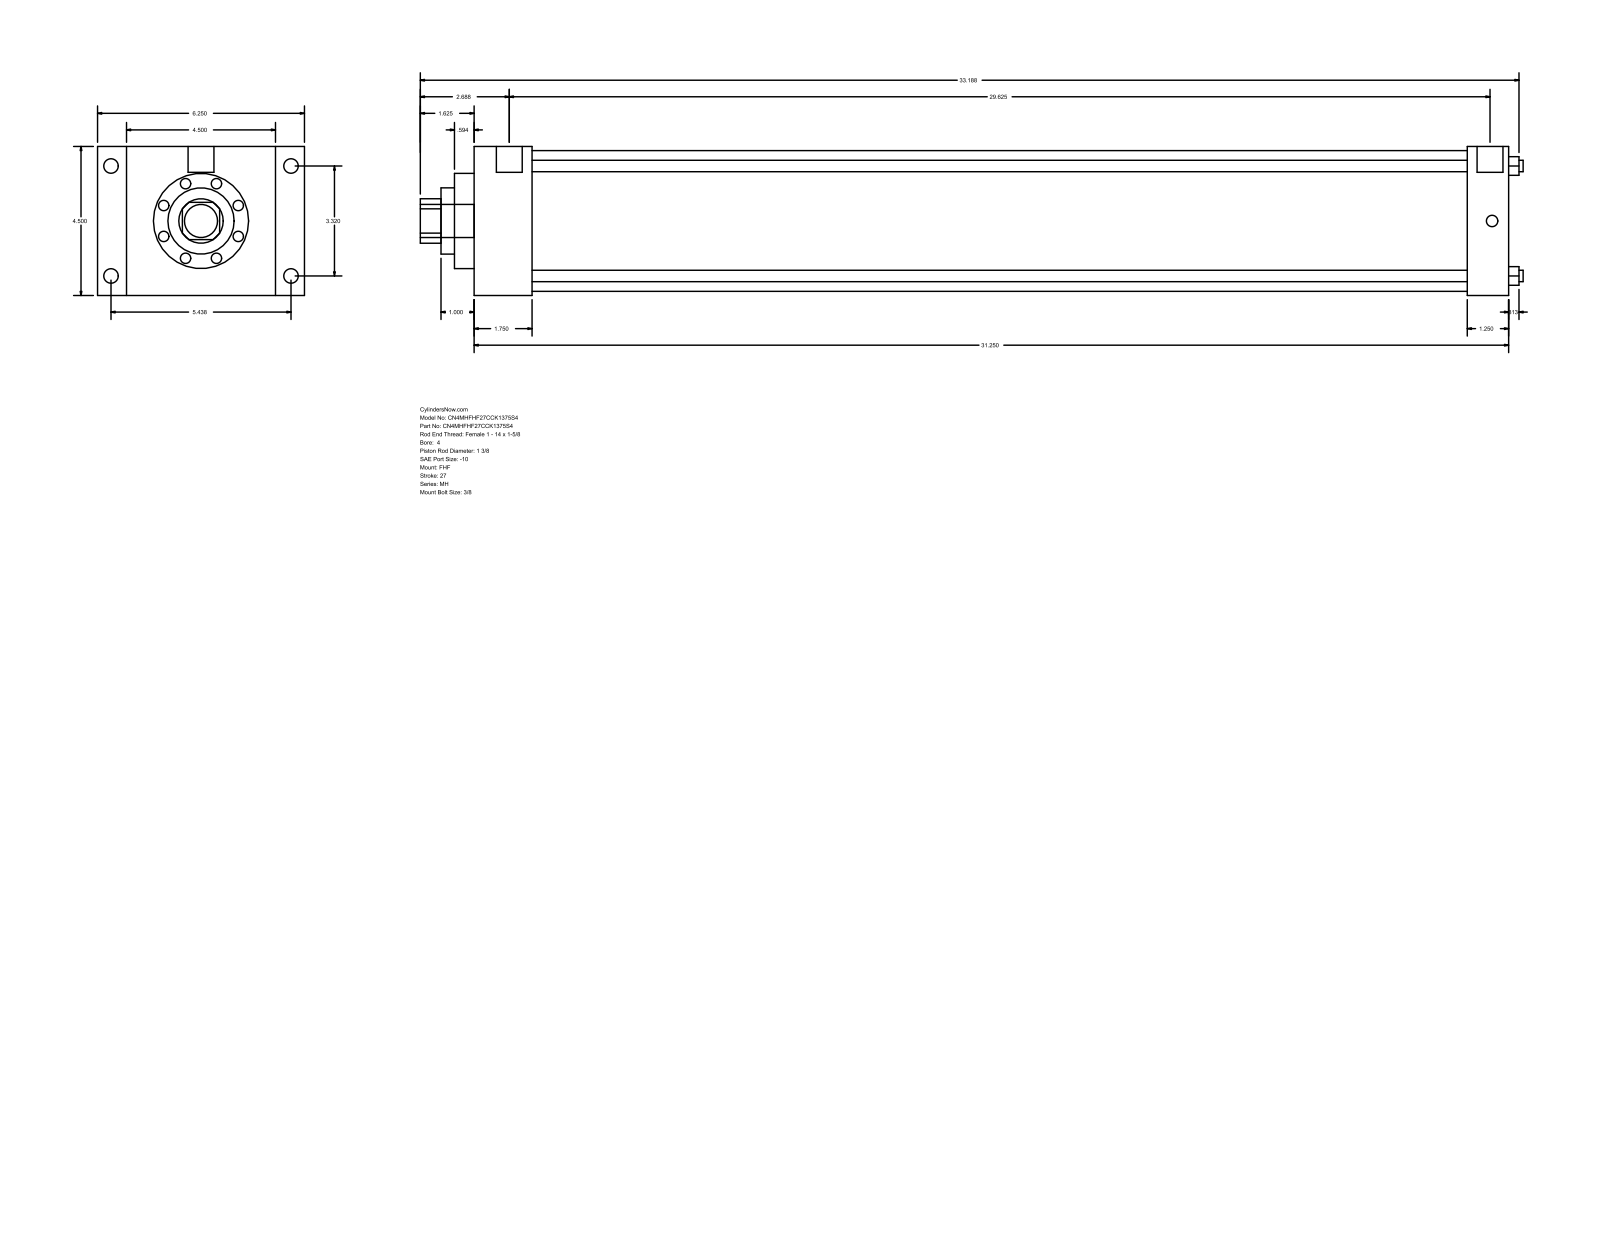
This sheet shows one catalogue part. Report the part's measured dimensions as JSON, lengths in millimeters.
{"part_name": "MH_FHF__0400_1.375", "step_written_by": "GSSL Pune (CONFIG_CONTROL_DESIGN)", "units": "millimeters", "bodies": {"solids": 0, "faces": 90, "planar": 61, "cylindrical": 29, "other": 0}, "overall_size": [846.14, 158.75, 114.3], "round_holes": [[8.76, 4], [34.92, 1], [50.8, 1], [73.03, 1], [107.95, 1]], "round_bosses_or_shafts": [[11.13, 4], [8.73, 4], [19.84, 2], [25.4, 1]], "partial_cylinders_radius": [[17.06, 1]], "face_to_face_distances": [114.3, 793.75, 44.45, 749.3, 22.23, 136.53, 158.76, 762, 717.55, 31.75], "hole_center_spacings": [59.62, 84.32, 119.25]}
